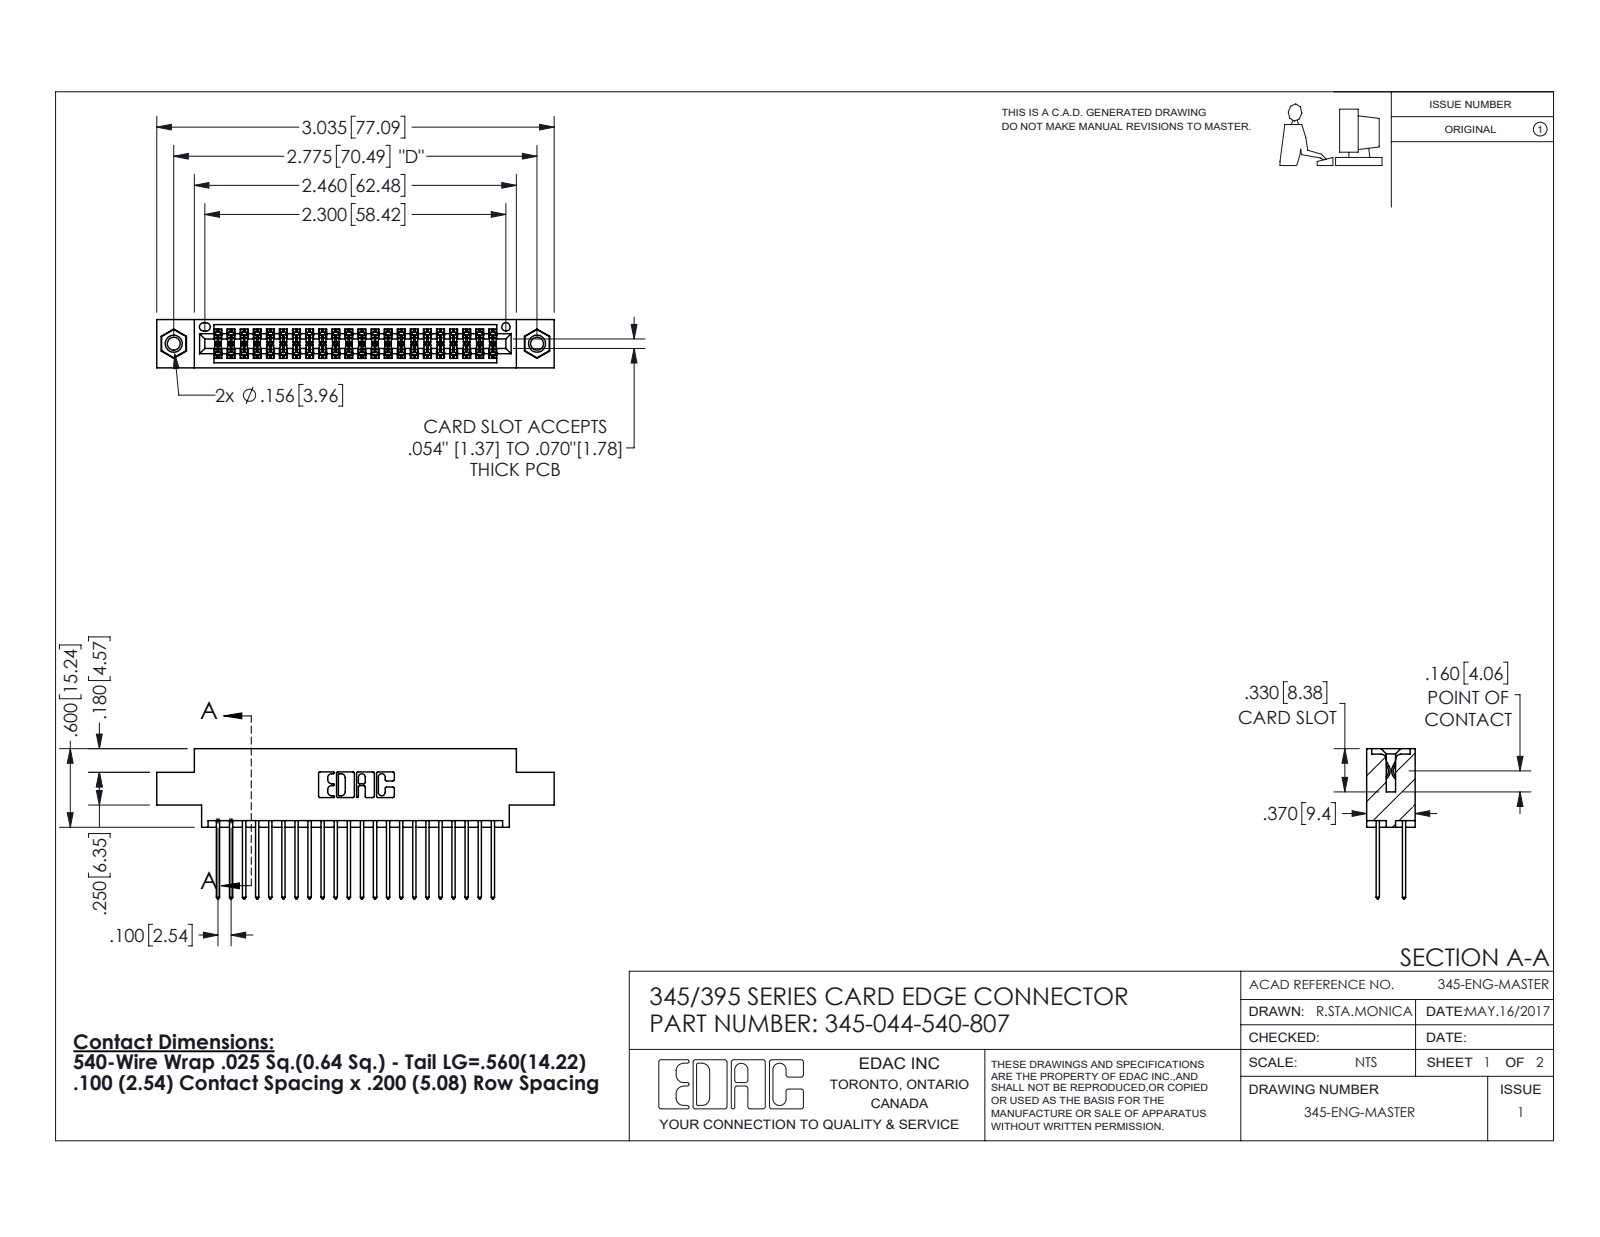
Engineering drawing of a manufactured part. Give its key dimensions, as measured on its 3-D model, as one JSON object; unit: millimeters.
{"part_name": "345-250-001_345-250-005-103; 345-292-001_345-293-140; 345 Part_0.170 Offset - 0.156 Dia-TI; 345-044-540-807", "step_written_by": "SolidWorks 2016 (CONFIG_CONTROL_DESIGN)", "units": "millimeters", "bodies": {"solids": 47, "faces": 2390, "planar": 1568, "cylindrical": 806, "other": 16}, "overall_size": [77.1, 29.1, 9.4], "volume_mm3": 7340, "surface_area_mm2": 11410, "round_holes": [[2.5, 2], [3.2, 2], [4, 2], [1.6, 1]], "round_bosses_or_shafts": [[3.9, 2]], "partial_cylinders_radius": [[0.2, 66], [0.3, 44], [0.3, 22], [0.2, 6], [0.8, 6], [0.7, 3], [0.4, 2], [0.5, 2]], "face_to_face_distances": [1.8, 7.6, 5.1, 2.5, 6.9, 0.6, 9.4, 5.7, 4.4, 3.8], "hole_center_spacings": [6.9, 64.5, 70.5]}
